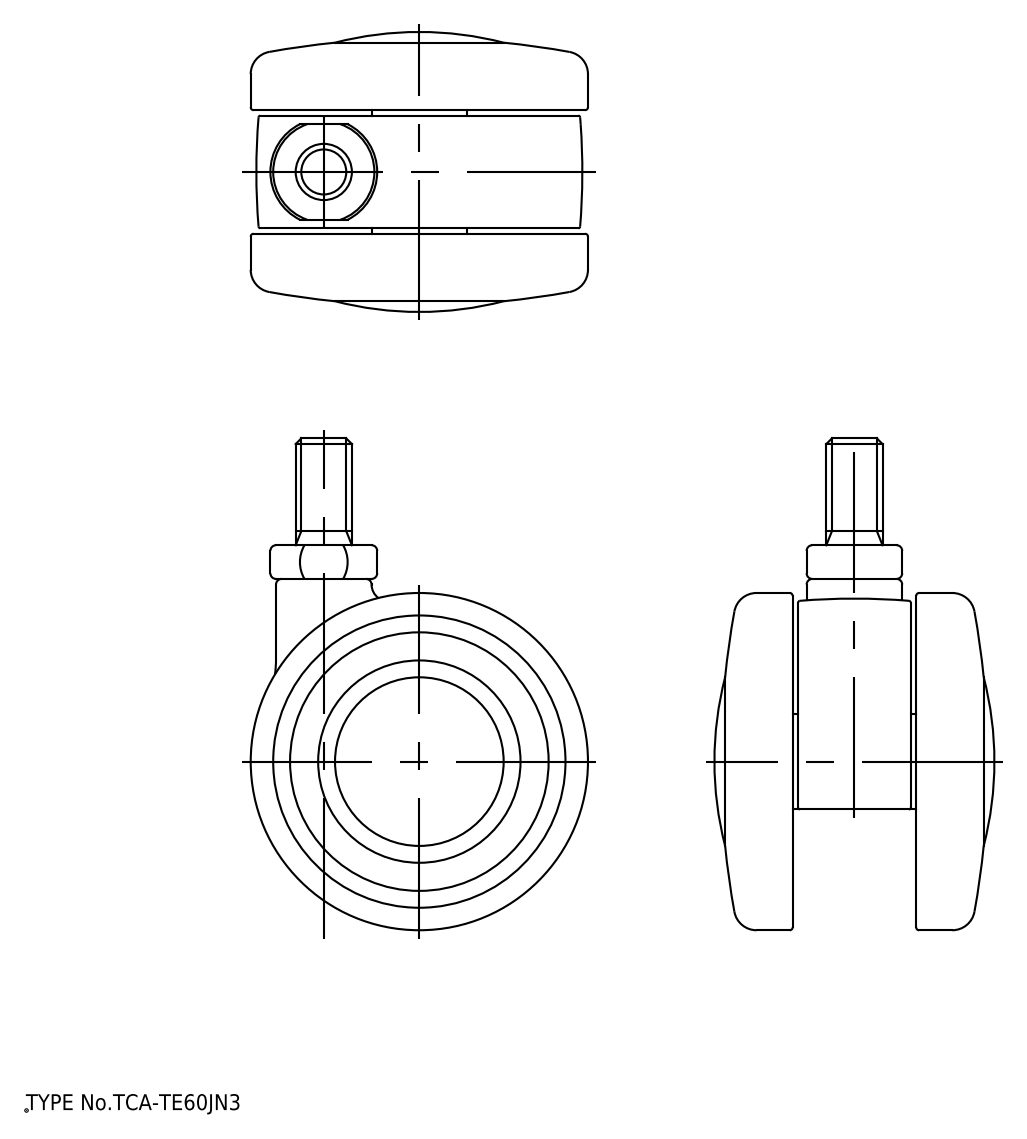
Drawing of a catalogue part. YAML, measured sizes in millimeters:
part_name: "TCA-TE60J_Body; TCA-TE60J_Wheel; TCA-TE60JN3_Shaft"
step_written_by: "spGate 18.9.1 (****-****-****-****) (AUTOMOTIVE_DESIGN)"
units: millimeters
bodies: {solids: 4, faces: 189, planar: 46, cylindrical: 75, other: 68}
overall_size: [87.5, 60, 49.14]
volume: 86320
surface_area: 31947
round_holes:
  - {diameter: 8, count: 1}
  - {diameter: 9.3, count: 1}
  - {diameter: 10.7, count: 1}
  - {diameter: 20, count: 1}
  - {diameter: 30.2, count: 1}
  - {diameter: 45, count: 1}
round_bosses_or_shafts:
  - {diameter: 60, count: 1}
  - {diameter: 36, count: 1}
  - {diameter: 29.9, count: 1}
  - {diameter: 18, count: 1}
  - {diameter: 17, count: 1}
  - {diameter: 10.5, count: 1}
  - {diameter: 10, count: 1}
  - {diameter: 6.5, count: 1}
partial_cylinders:
  - {radius: 0.3, count: 5}
  - {radius: 1, count: 3}
  - {radius: 2, count: 3}
  - {radius: 10, count: 1}
  - {radius: 10.5, count: 1}
  - {radius: 26.5, count: 1}
  - {radius: 29, count: 1}
face_to_face_distances: [2, 19, 7, 5, 24, 26, 11, 30.5, 28.5, 0.5]
